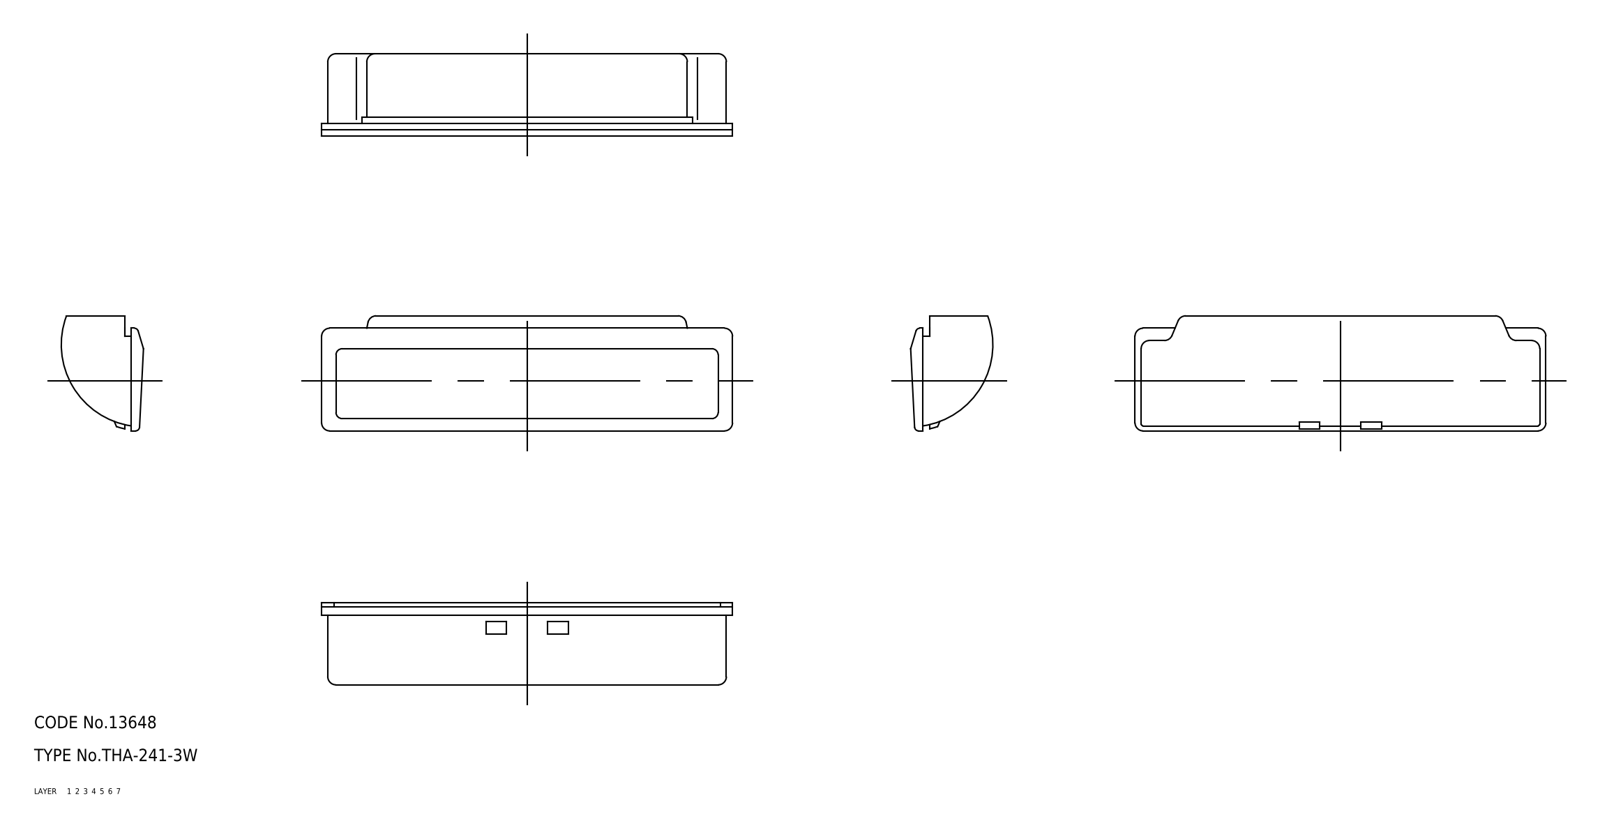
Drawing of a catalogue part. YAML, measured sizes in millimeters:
part_name: "pull; THA_241_3W"
step_written_by: "SolidWorks 2015 (AUTOMOTIVE_DESIGN)"
units: millimeters
bodies: {solids: 1, faces: 88, planar: 32, cylindrical: 34, other: 22}
overall_size: [100, 28, 19.99]
volume: 12342
surface_area: 13016
partial_cylinders:
  - {radius: 2, count: 11}
  - {radius: 1, count: 9}
  - {radius: 1.5, count: 6}
  - {radius: 3, count: 1}
  - {radius: 18, count: 1}
  - {radius: 18.68, count: 1}
  - {radius: 20, count: 1}
  - {radius: 21, count: 1}
face_to_face_distances: [1.3, 2, 1.6, 1.5, 3, 6.7, 8, 95, 3.1, 5]
